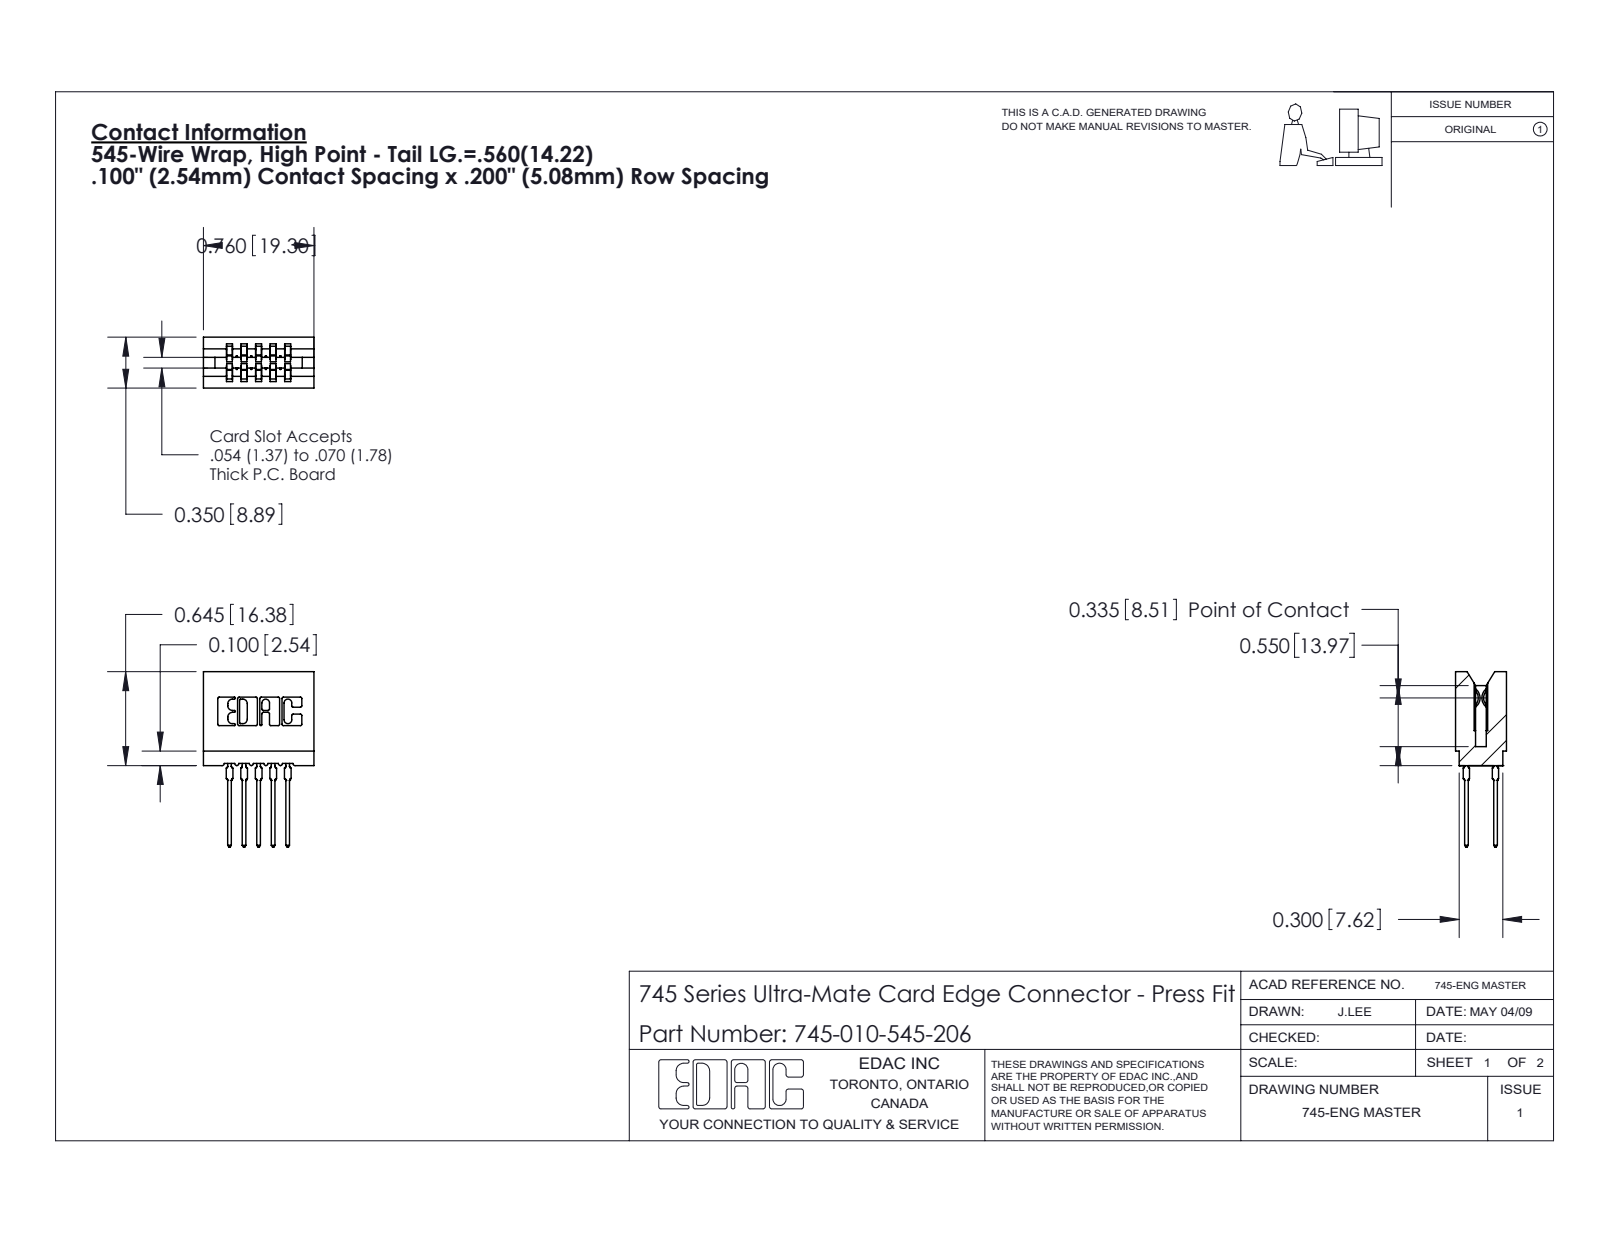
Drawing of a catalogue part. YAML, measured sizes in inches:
part_name: "745-292-001_545; 745 Part_Insulator Option - 06; 745-010-545-206"
step_written_by: "SolidWorks 2020 (CONFIG_CONTROL_DESIGN)"
units: inches
bodies: {solids: 11, faces: 991, planar: 516, cylindrical: 215, other: 260}
overall_size: [1.206, 0.76, 0.35]
volume: 0.121
surface_area: 5.173
partial_cylinders:
  - {radius: 0.01, count: 22}
  - {radius: 0.021, count: 20}
  - {radius: 0.015, count: 10}
  - {radius: 0.005, count: 8}
  - {radius: 0.011, count: 8}
  - {radius: 0.007, count: 6}
  - {radius: 0.031, count: 6}
  - {radius: 0.026, count: 3}
face_to_face_distances: [0.1, 0.2, 0.042, 0.3, 0.142, 0.058, 0.287, 0.35, 0.063, 0.242]
